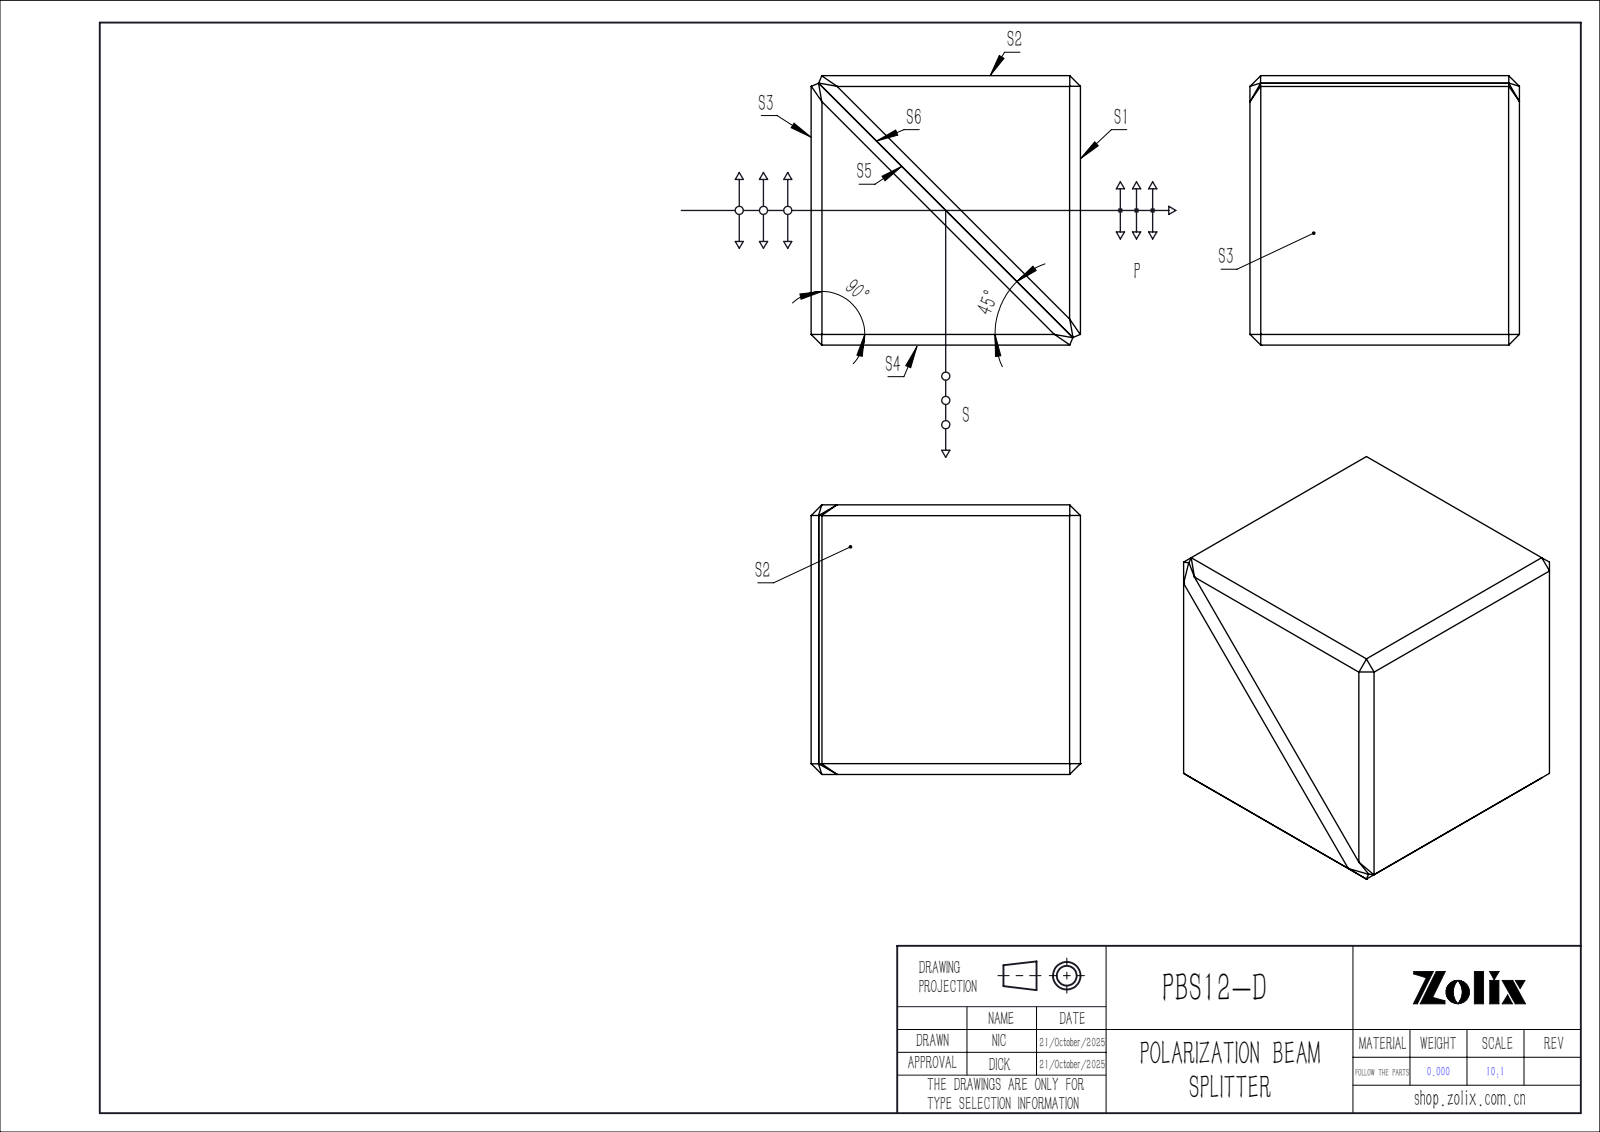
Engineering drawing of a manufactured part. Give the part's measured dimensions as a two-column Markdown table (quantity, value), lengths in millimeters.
| quantity | value |
| --- | --- |
| part name | PBS621-1; PBS614-1-2; PBS614-1-1 |
| STEP written by | SolidWorks 2022 (CONFIG_CONTROL_DESIGN) |
| units | millimeters |
| bodies | 2 solids, 43 faces (41 planar, 2 cylindrical, 0 other) |
| overall size | 12.7 × 12.7 × 12.7 |
| volume | 2 044 mm³ |
| surface area | 1 388 mm² |
| round holes (diameter × count) | 0.2 × 1 |
| main face-to-face distances | 12.7, 17.67, 8.7, 17.68, 8.84, 8.83, 16.22, 16.23, 18.81, 21.52 |
